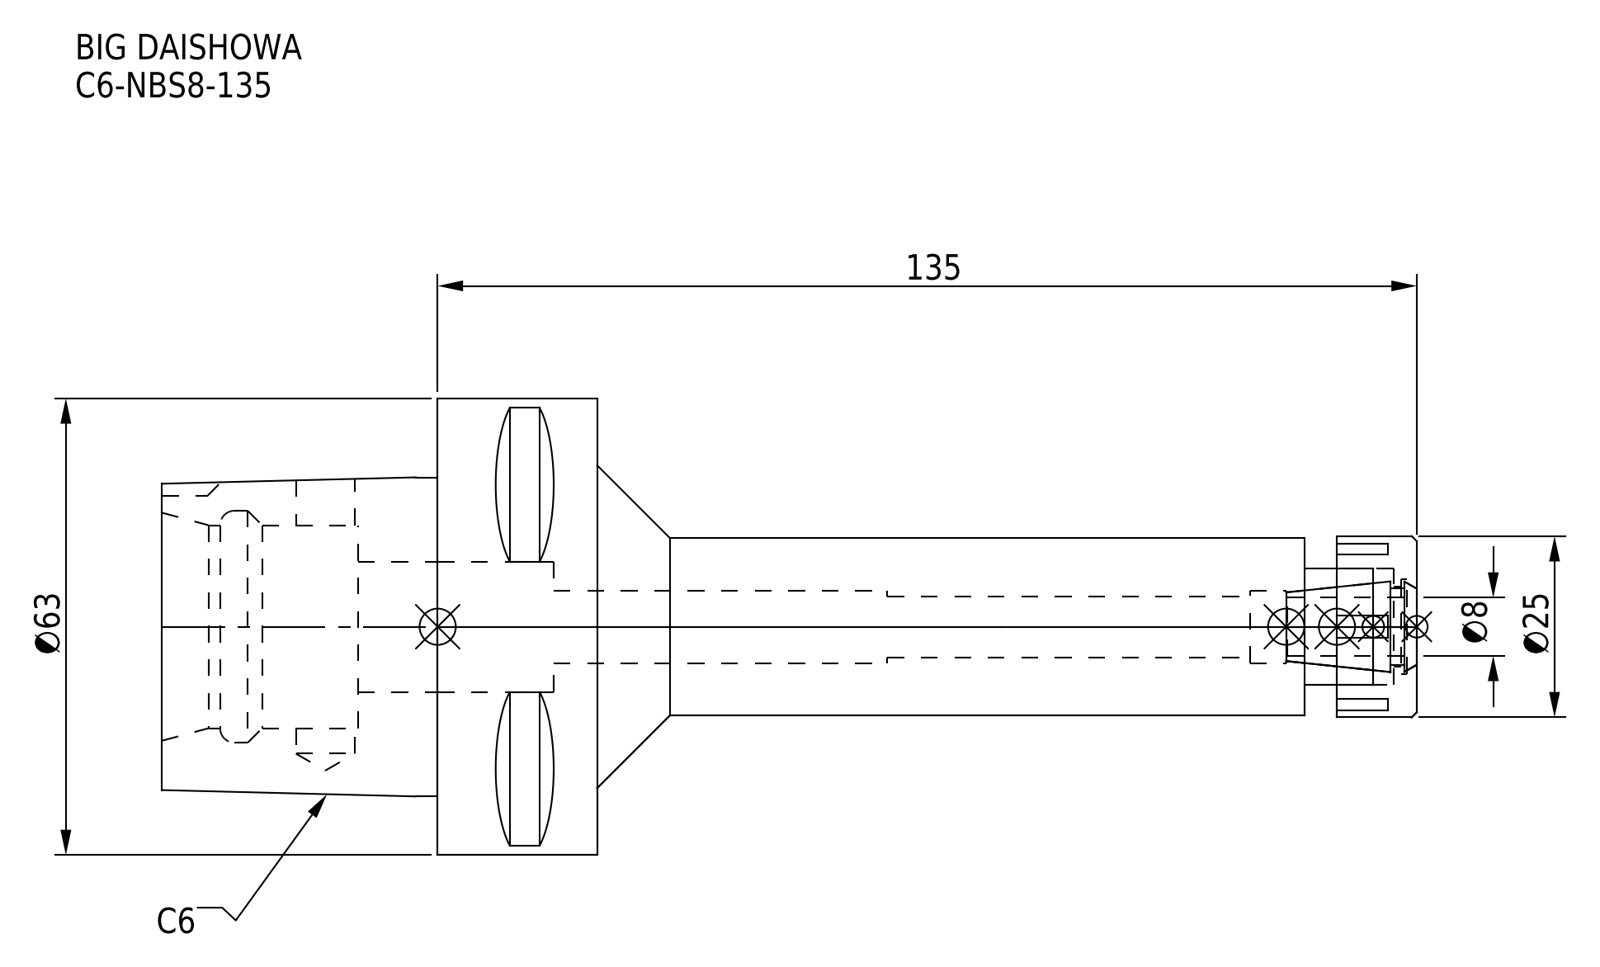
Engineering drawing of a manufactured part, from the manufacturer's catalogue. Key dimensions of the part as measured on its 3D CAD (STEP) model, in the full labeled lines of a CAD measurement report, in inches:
Part name (STEP PRODUCT): C6-NBS8-135.stp; C6-NBS8-135-080_ASM.stp; C6-NBS8-135; C6-NBS8-135-FreeParts (+3 more)
STEP written by: SolidWorks 2019 (CONFIG_CONTROL_DESIGN)
Units: inches
Bodies: 2 solids, 112 faces (61 planar, 33 cylindrical, 18 other)
Overall size (bounding box): 6.811 × 2.48 × 2.48
Volume: 8.835 in³ · Surface area: 51.64 in²
Round holes (diameter × count): ⌀0.319 ×1, ⌀0.331 ×1, ⌀0.394 ×1, ⌀0.433 ×1, ⌀0.512 ×1, ⌀0.63 ×1, ⌀0.709 ×1, ⌀1.102 ×1, ⌀1.26 ×1
Round bosses / shafts (diameter × count): ⌀2.48 ×1, ⌀0.984 ×1, ⌀0.965 ×1
Partial cylindrical surfaces — rounded edges, fillets, slot ends (radius × count): R0.197 ×1
Main face-to-face distances: 0.866, 0.433, 5.315, 1.063, 2.362, 1.496, 4.449, 1.299, 5.748, 6.811
